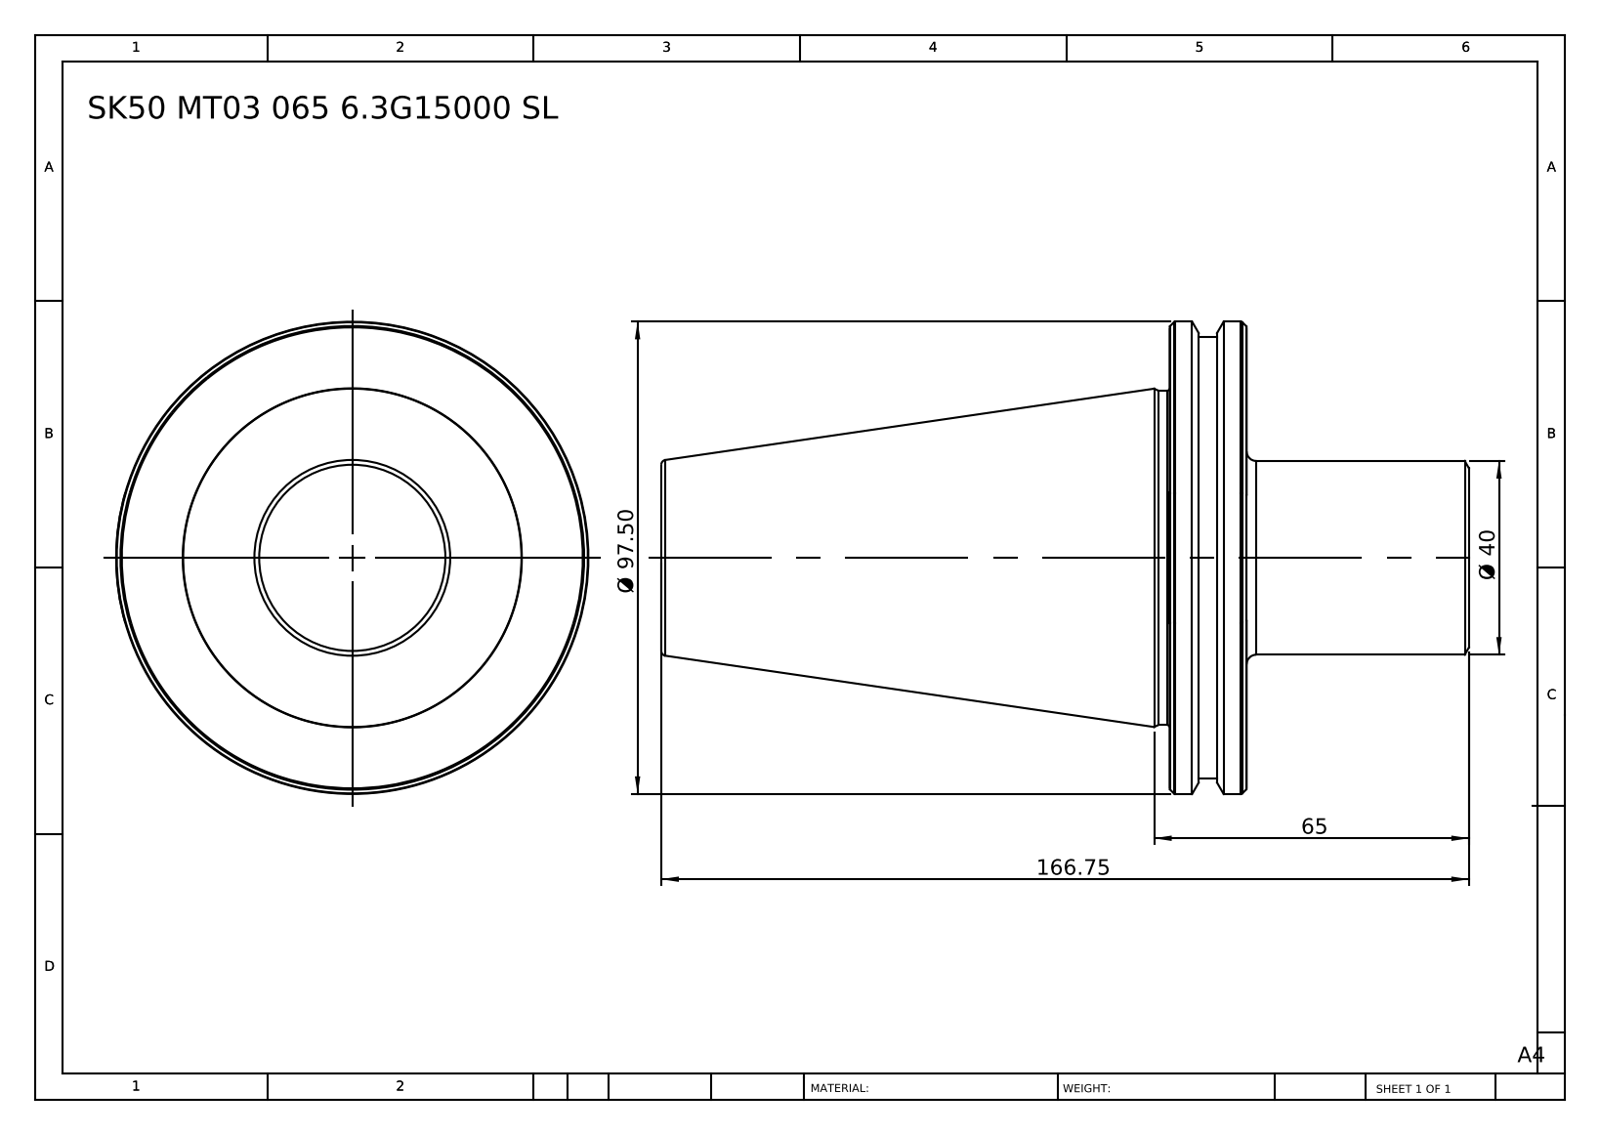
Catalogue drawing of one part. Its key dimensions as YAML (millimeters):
part_name: "SK 50 MT03 065 6.3G15000 SL"
step_written_by: "SolidWorks 2014 (CONFIG_CONTROL_DESIGN)"
units: millimeters
bodies: {solids: 1, faces: 64, planar: 6, cylindrical: 10, other: 48}
overall_size: [166.75, 97.5, 97.5]
volume: 431218
surface_area: 42167
round_bosses_or_shafts:
  - {diameter: 97.5, count: 1}
  - {diameter: 91, count: 1}
  - {diameter: 69, count: 1}
  - {diameter: 40, count: 1}
face_to_face_distances: [15.9, 120.85, 104.95, 45.9, 61.8, 166.75, 52, 6.1, 9.8, 114.75]
